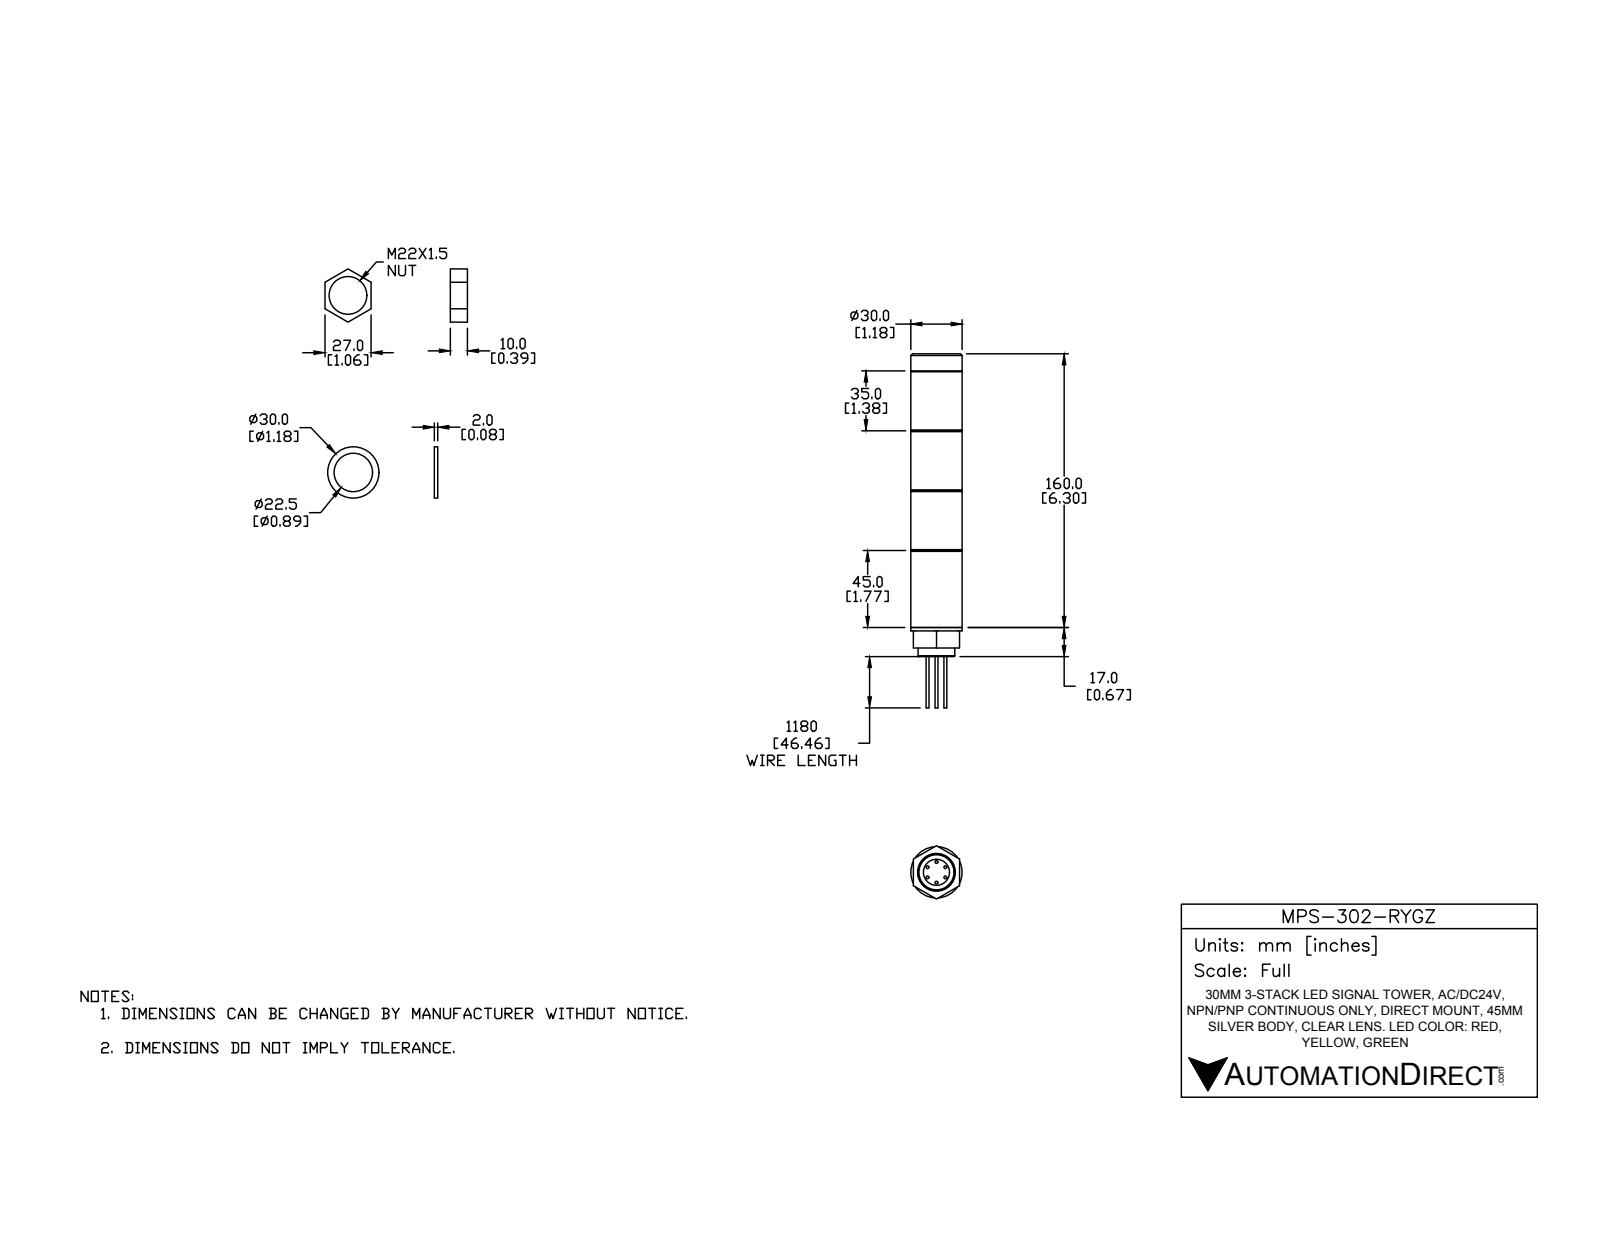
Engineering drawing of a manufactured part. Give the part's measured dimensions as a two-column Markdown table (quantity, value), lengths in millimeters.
| quantity | value |
| --- | --- |
| part name | MPS-302-RYGZ |
| STEP written by | SolidWorks 2016 (AUTOMOTIVE_DESIGN) |
| units | millimeters |
| bodies | 14 solids, 111 faces (51 planar, 40 cylindrical, 20 other) |
| overall size | 207 × 31.18 × 30 |
| volume | 109 034 mm³ |
| surface area | 32 238 mm² |
| round holes (diameter × count) | 3.2 × 1, 7.7 × 1, 15.3 × 1, 20.7 × 1, 22 × 1 |
| round bosses / shafts (diameter × count) | 1.7 × 6, 30 × 1, 21.5 × 1, 5 × 1 |
| main face-to-face distances | 35, 70, 45, 80, 115, 105, 47, 82, 117, 162 |
